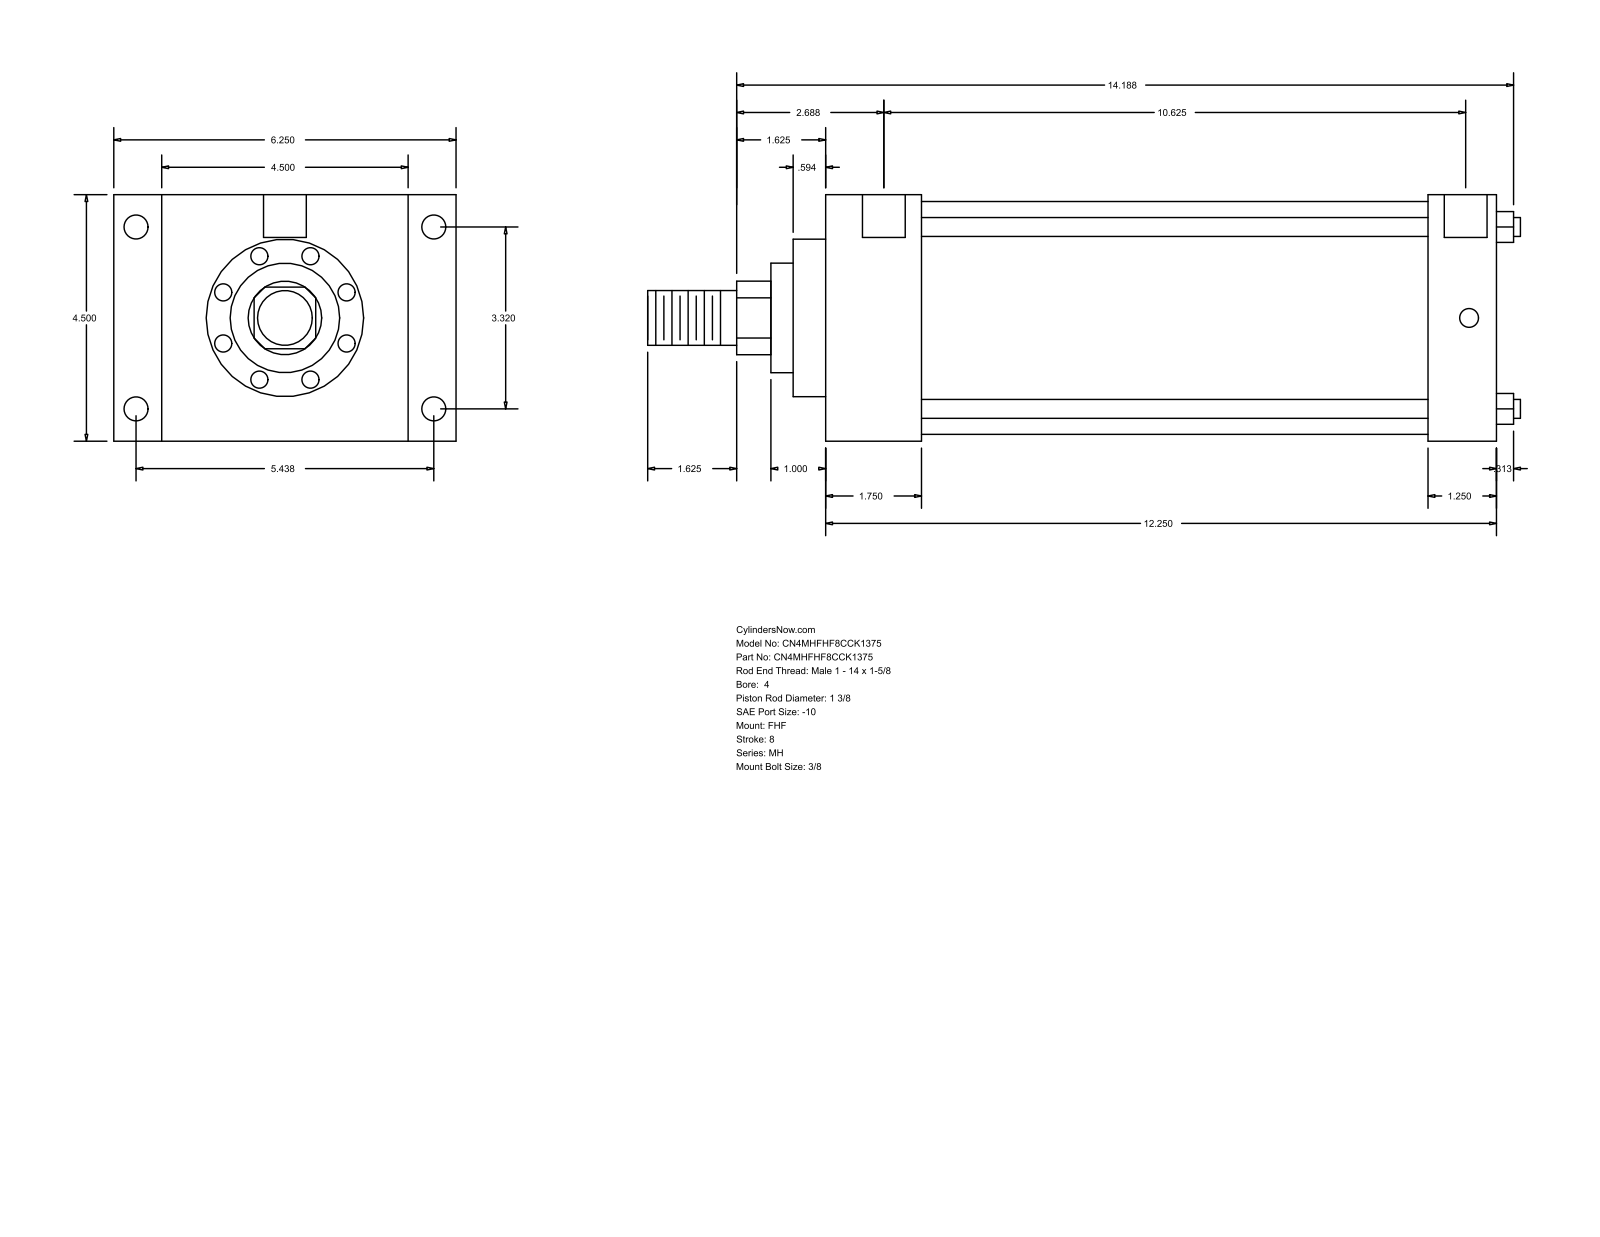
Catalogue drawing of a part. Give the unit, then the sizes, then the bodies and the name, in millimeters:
Units: millimetres
Overall size (bounding box): 404.81 × 158.75 × 114.3
Round holes (diameter × count): ⌀8.73 ×4, ⌀11.13 ×4, ⌀19.84 ×2
Round bosses / shafts (diameter × count): ⌀8.76 ×4, ⌀107.95 ×1, ⌀73.03 ×1, ⌀50.8 ×1, ⌀34.92 ×1, ⌀25.4 ×1
Partial cylindrical surfaces — rounded edges, fillets, slot ends (radius × count): R17.06 ×1
Main face-to-face distances: 114.3, 311.16, 44.45, 266.71, 22.23, 136.53, 158.76, 279.41, 234.96, 31.75
Hole centre spacings: 1.59, 84.32, 138.12, 161.82, 271.47, 273.06, 269.88
Bodies: 0 solids, 90 faces (61 planar, 29 cylindrical, 0 other)
Part name (STEP PRODUCT): MH_FHF__0400_1.375
STEP written by: GSSL Pune (CONFIG_CONTROL_DESIGN)
